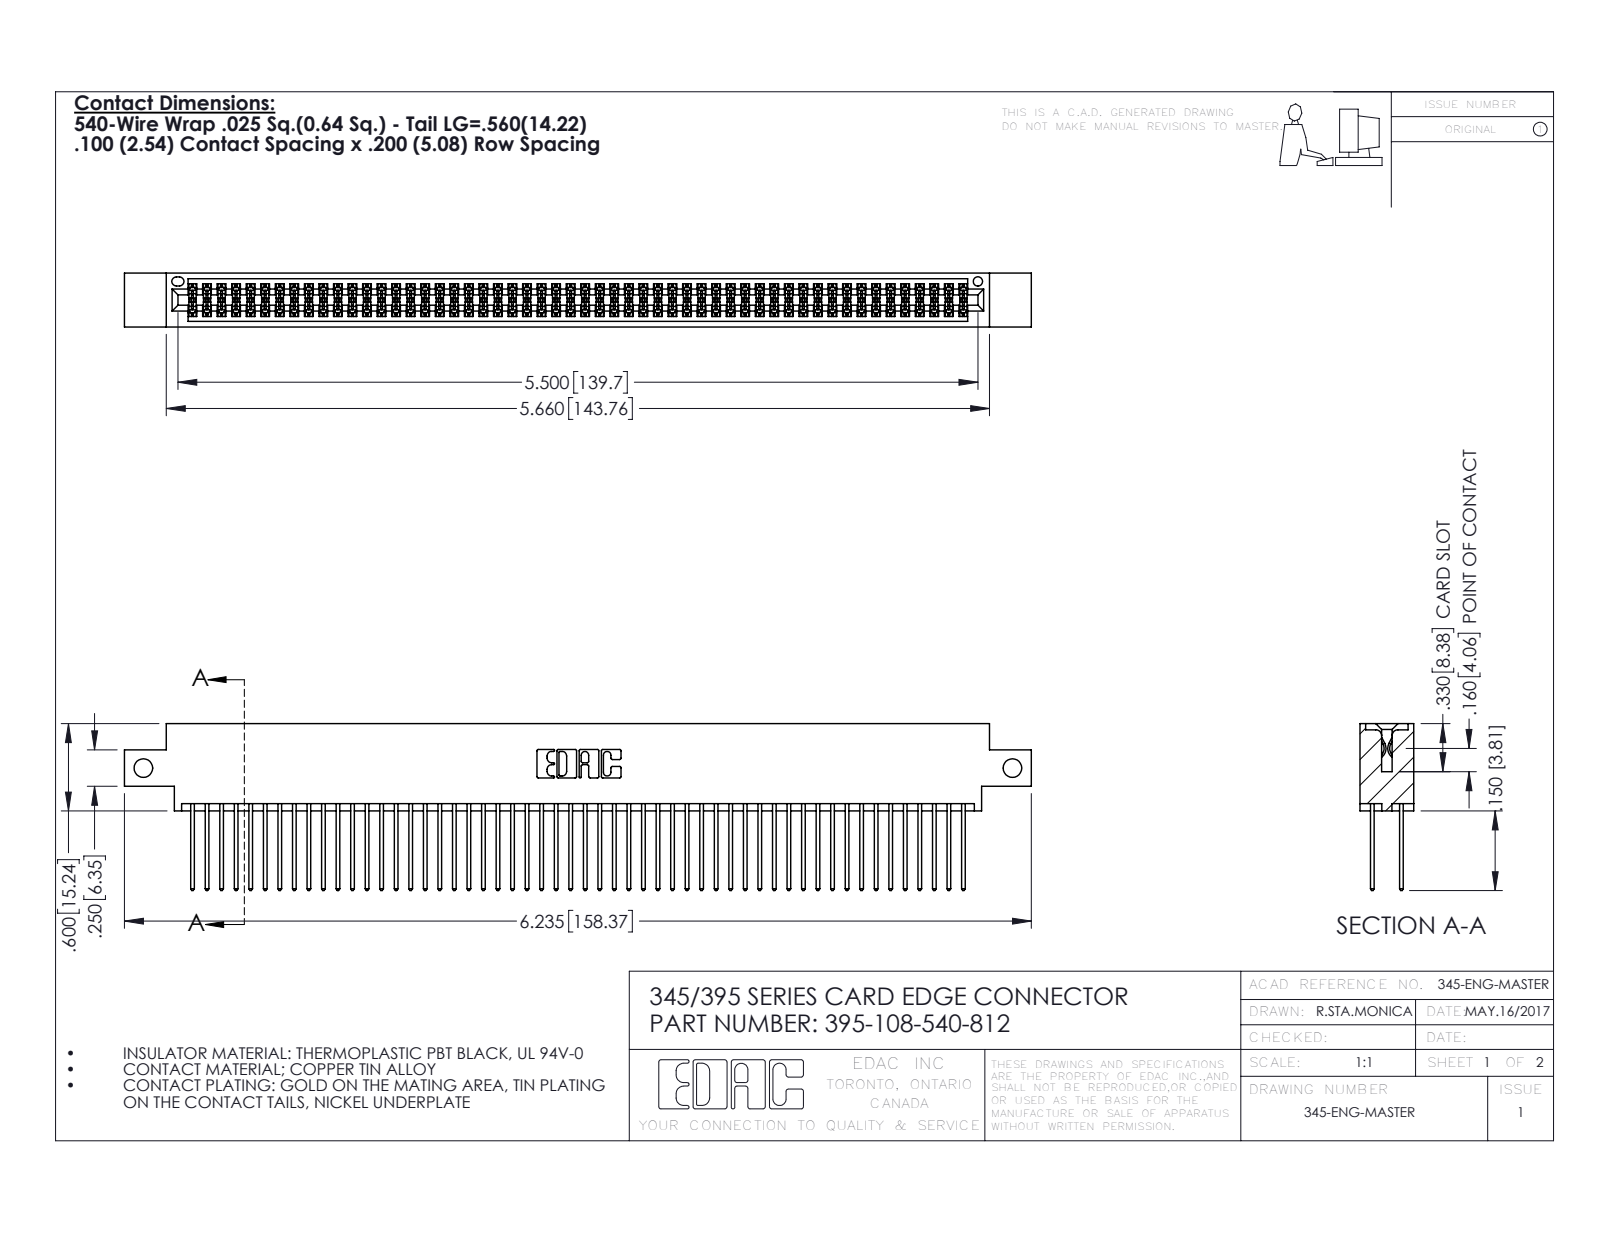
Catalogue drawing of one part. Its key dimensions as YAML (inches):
part_name: "395-108-540-812; 345 Part_0.170 Offset - Side Mount; 345-292-001_345-293-140"
step_written_by: "SolidWorks 2016 (CONFIG_CONTROL_DESIGN)"
units: inches
bodies: {solids: 109, faces: 5530, planar: 3648, cylindrical: 1882, other: 0}
overall_size: [6.235, 1.147, 0.37]
volume: 0.958
surface_area: 39.3
round_holes:
  - {diameter: 0.128, count: 2}
  - {diameter: 0.064, count: 1}
partial_cylinders:
  - {radius: 0.006, count: 162}
  - {radius: 0.01, count: 108}
  - {radius: 0.01, count: 22}
  - {radius: 0.007, count: 6}
  - {radius: 0.031, count: 6}
  - {radius: 0.026, count: 3}
  - {radius: 0.014, count: 2}
  - {radius: 0.019, count: 2}
face_to_face_distances: [0.072, 0.298, 0.2, 0.098, 0.272, 0.025, 0.37, 0.225, 0.175, 0.149]
hole_center_spacings: [5.975]
